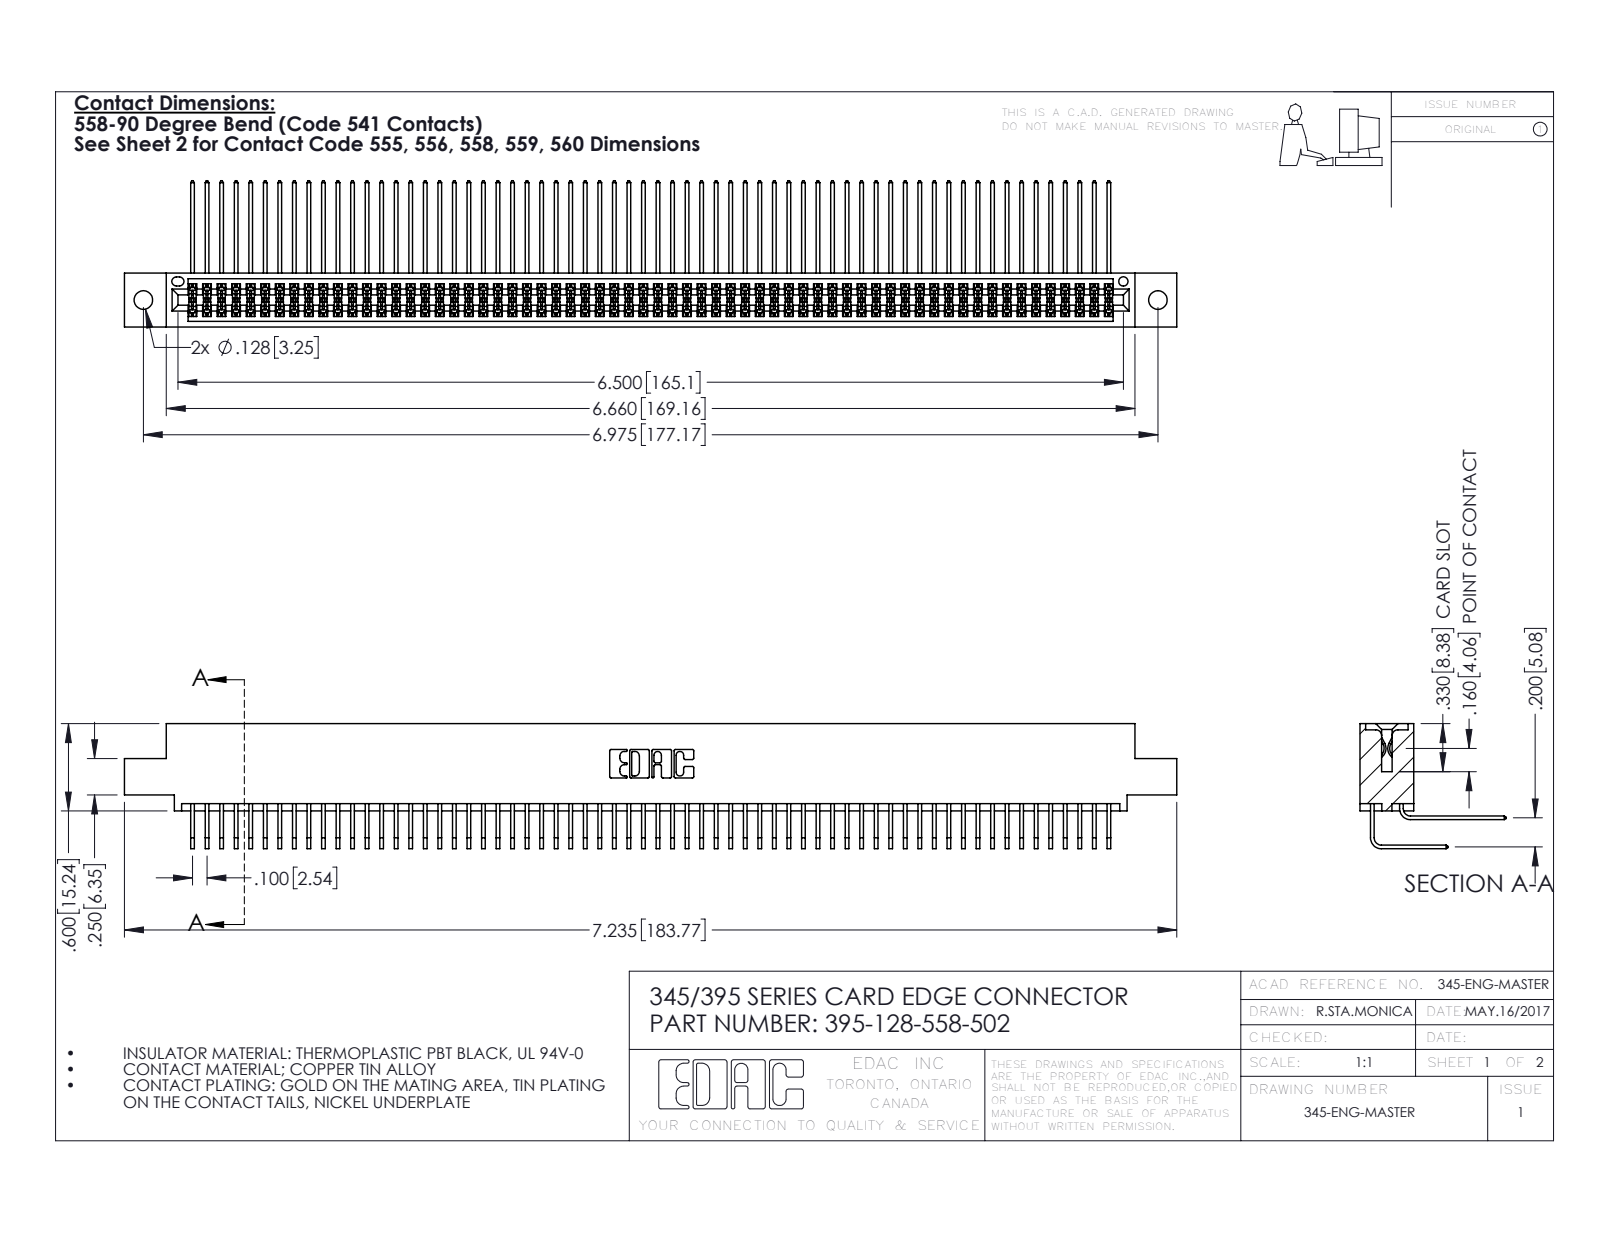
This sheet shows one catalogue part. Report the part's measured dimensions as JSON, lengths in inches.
{"part_name": "395-128-558-502; 345-292-001_558 Tail - 2; 345 Part_0.110 Offset - 0.128 Dia; 345-292-001_558 559 Tail - 1", "step_written_by": "SolidWorks 2016 (CONFIG_CONTROL_DESIGN)", "units": "inches", "bodies": {"solids": 129, "faces": 6786, "planar": 4564, "cylindrical": 2222, "other": 0}, "overall_size": [7.235, 1.005, 0.859], "volume_in3": 1.14, "surface_area_in2": 48.57, "round_holes": [[0.128, 2], [0.064, 1]], "partial_cylinders_radius": [[0.006, 193], [0.01, 22], [0.007, 6], [0.031, 6], [0.026, 3], [0.014, 2], [0.019, 2], [0.022, 2]], "face_to_face_distances": [0.072, 0.298, 0.2, 0.37, 0.098, 0.272, 0.025, 0.225, 0.025, 0.175], "hole_center_spacings": [0.27, 6.739, 6.975]}
